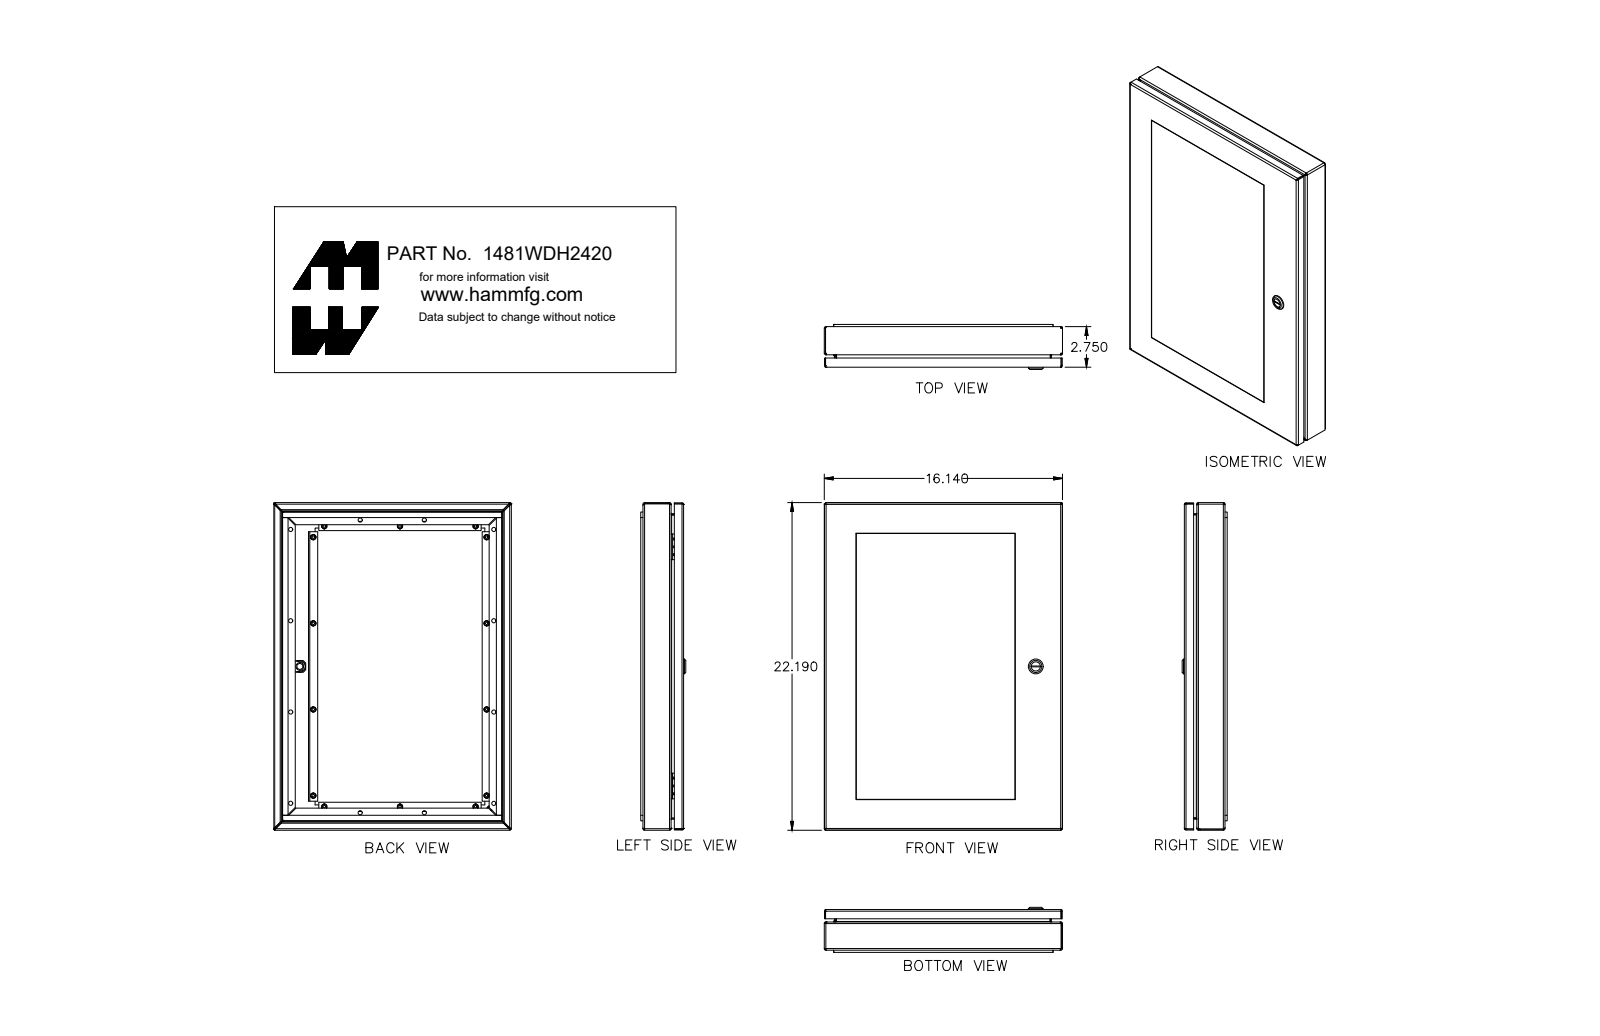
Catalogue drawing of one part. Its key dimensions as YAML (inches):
part_name: "1481WDH2420_Default"
step_written_by: "SolidWorks 2019 (CONFIG_CONTROL_DESIGN)"
units: inches
bodies: {solids: 49, faces: 1140, planar: 607, cylindrical: 327, other: 206}
overall_size: [22.19, 16.14, 2.91]
volume: 94.55
surface_area: 1698
round_holes:
  - {diameter: 0.13, count: 14}
  - {diameter: 0.281, count: 12}
  - {diameter: 0.136, count: 2}
  - {diameter: 0.232, count: 1}
  - {diameter: 0.24, count: 1}
  - {diameter: 0.242, count: 1}
  - {diameter: 0.625, count: 1}
  - {diameter: 0.785, count: 1}
round_bosses_or_shafts:
  - {diameter: 0.368, count: 14}
  - {diameter: 0.226, count: 14}
  - {diameter: 0.164, count: 14}
  - {diameter: 1.1, count: 1}
  - {diameter: 0.525, count: 1}
  - {diameter: 0.455, count: 1}
  - {diameter: 0.398, count: 1}
  - {diameter: 0.356, count: 1}
partial_cylinders:
  - {radius: 0.036, count: 28}
  - {radius: 0.101, count: 28}
  - {radius: 0.108, count: 28}
  - {radius: 0.016, count: 4}
  - {radius: 0.088, count: 4}
  - {radius: 0.125, count: 2}
  - {radius: 0.021, count: 1}
  - {radius: 0.029, count: 1}
face_to_face_distances: [0.072, 0.25, 0.178, 2.578, 2.328, 0.842, 1.736, 0.592, 16.068, 2.65]
hole_center_spacings: [4.75, 5.833, 6.182, 9.078, 11.026, 11.335, 11.75, 13.119]
